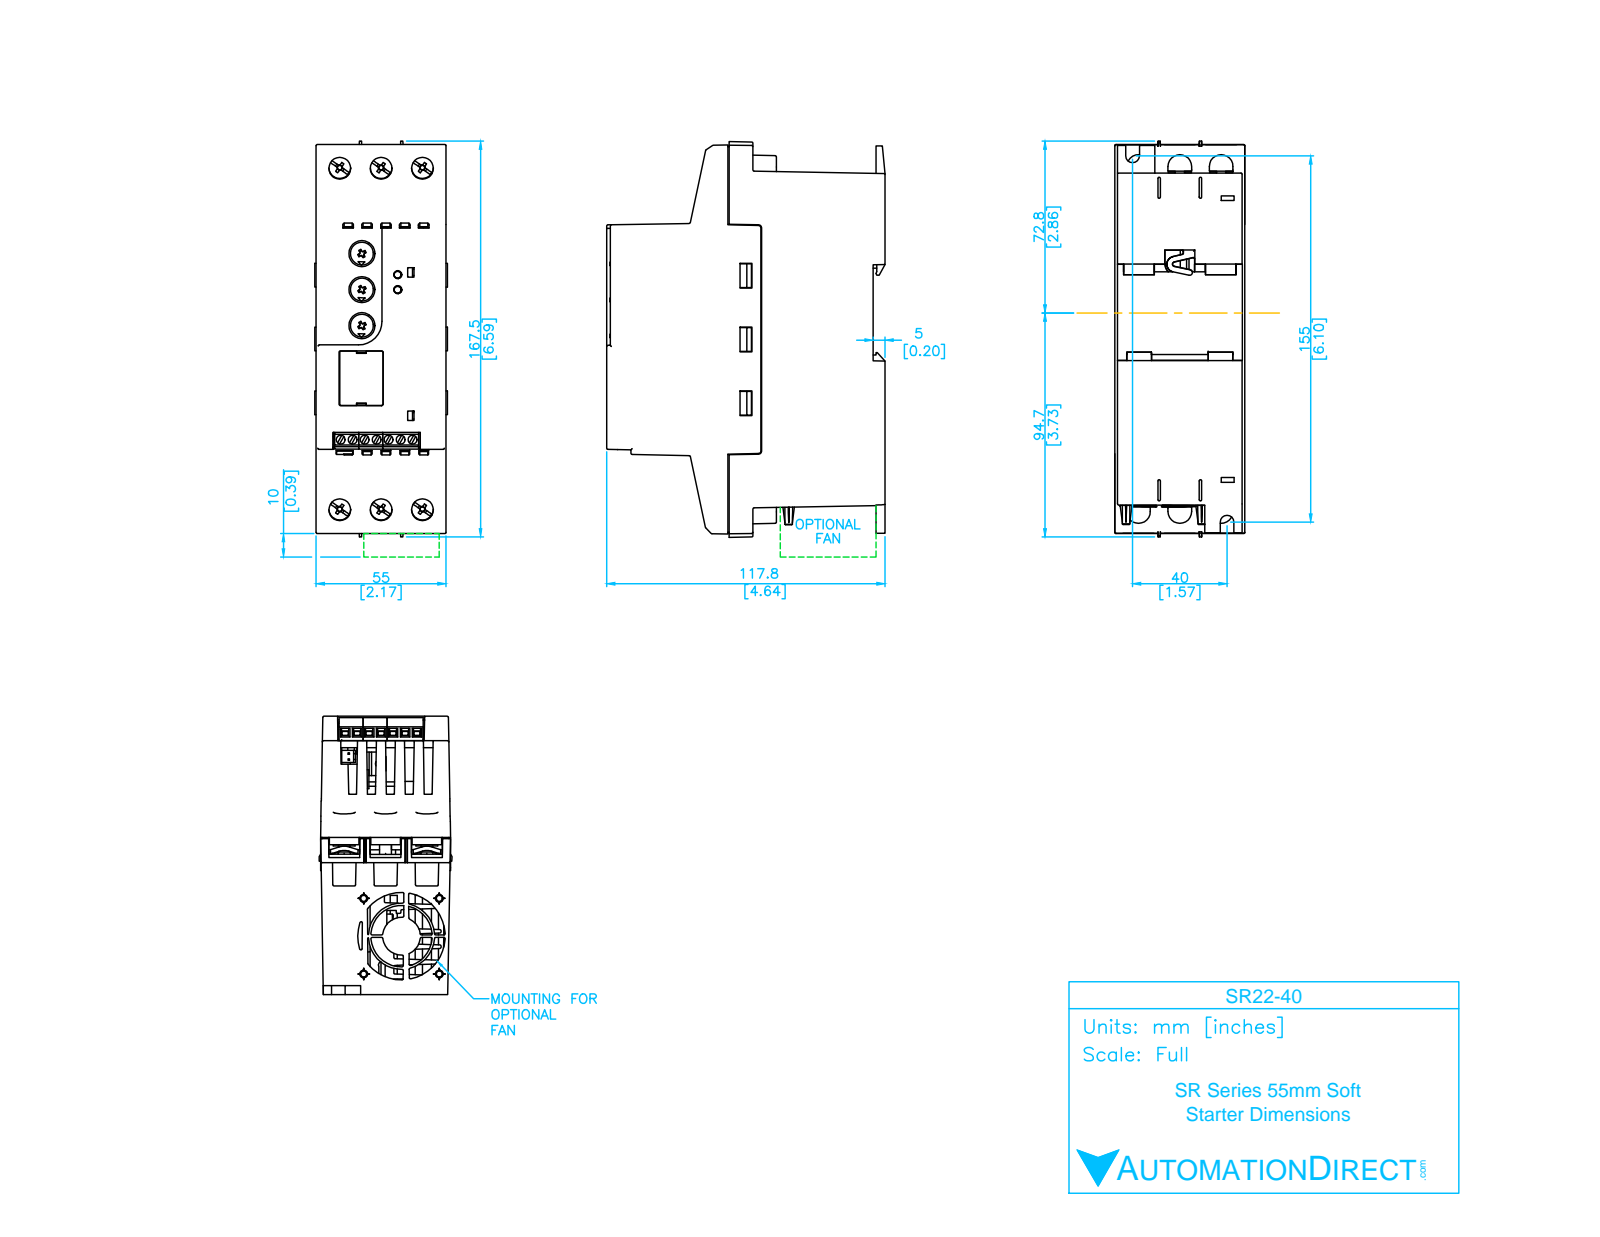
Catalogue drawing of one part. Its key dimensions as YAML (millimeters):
part_name: "SR22-40"
step_written_by: "SolidWorks 2013 (AUTOMOTIVE_DESIGN)"
units: millimeters
bodies: {solids: 1, faces: 623, planar: 483, cylindrical: 110, other: 30}
overall_size: [164.5, 117.8, 55.87]
volume: 813460
surface_area: 69575
round_holes:
  - {diameter: 3.5, count: 7}
  - {diameter: 9.5, count: 6}
  - {diameter: 11.3, count: 3}
  - {diameter: 4, count: 2}
  - {diameter: 27.66, count: 1}
  - {diameter: 40.29, count: 1}
round_bosses_or_shafts:
  - {diameter: 10.44, count: 3}
  - {diameter: 29.09, count: 1}
  - {diameter: 16, count: 1}
partial_cylinders:
  - {radius: 0.5, count: 35}
  - {radius: 4.88, count: 6}
  - {radius: 1, count: 2}
  - {radius: 2.75, count: 2}
  - {radius: 10, count: 1}
face_to_face_distances: [54.97, 54.94, 55, 117.8, 5.14, 112.66, 141.5, 18, 0.5, 1.5]
hole_center_spacings: [5.25, 10.5, 15.75, 18, 137.19, 21, 136, 15]
